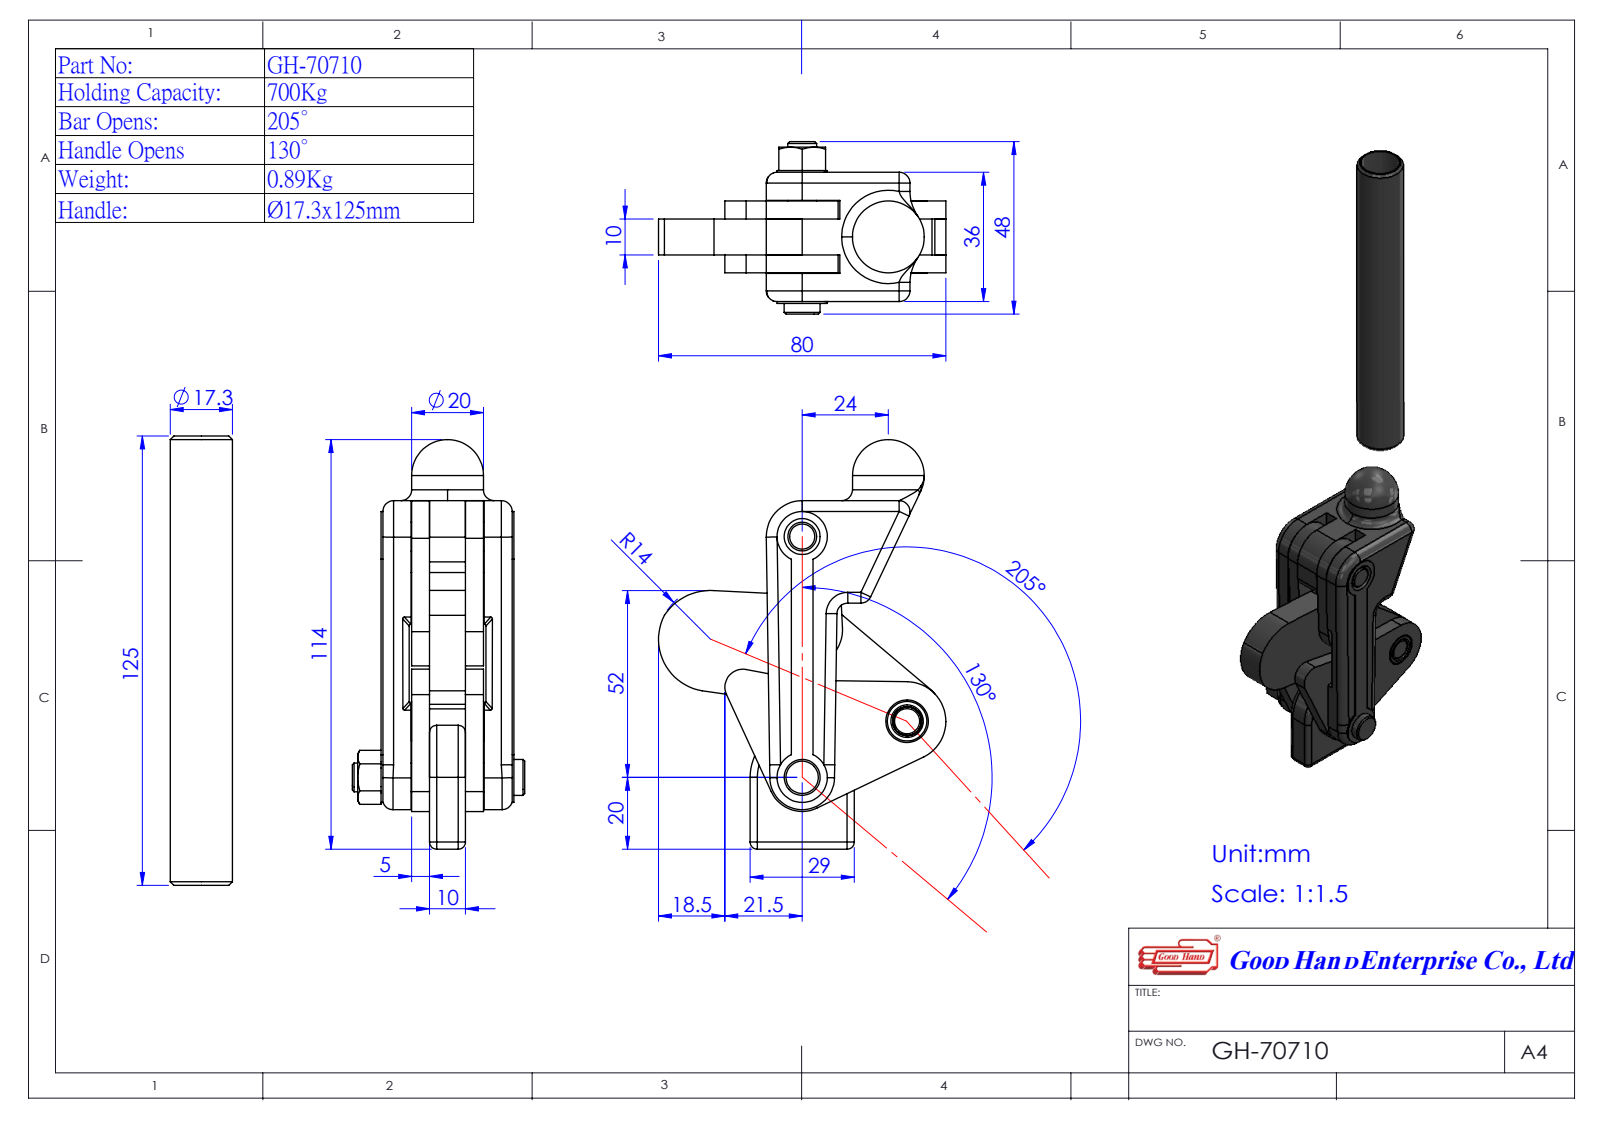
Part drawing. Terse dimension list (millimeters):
name: GH-70710(簡化); Group2^GH-70710(簡化); 17030501-1; Group4^GH-70710(簡化) (+3 more)
written by: SolidWorks 2016 (AUTOMOTIVE_DESIGN)
unit: mm
bodies: 6 solids, 206 faces (75 planar, 94 cylindrical, 37 other)
size: 239.35 × 80 × 46.5
volume: 117 003 mm³; area: 49 235 mm²
holes: 4× ⌀6, 1× ⌀12.5
bosses: 2× ⌀14, 1× ⌀20, 1× ⌀17.5, 1× ⌀10
rounds: 14× R3, 4× R10, 2× R5, 1× R9, 1× R9.5, 1× R11, 1× R11, 1× R11.17
face distances: 10, 15, 5, 5.15, 15.15, 20.15, 20, 13, 20.3, 8
hole spacings: 26, 33.12, 37.77, 41.05, 59.09, 67
